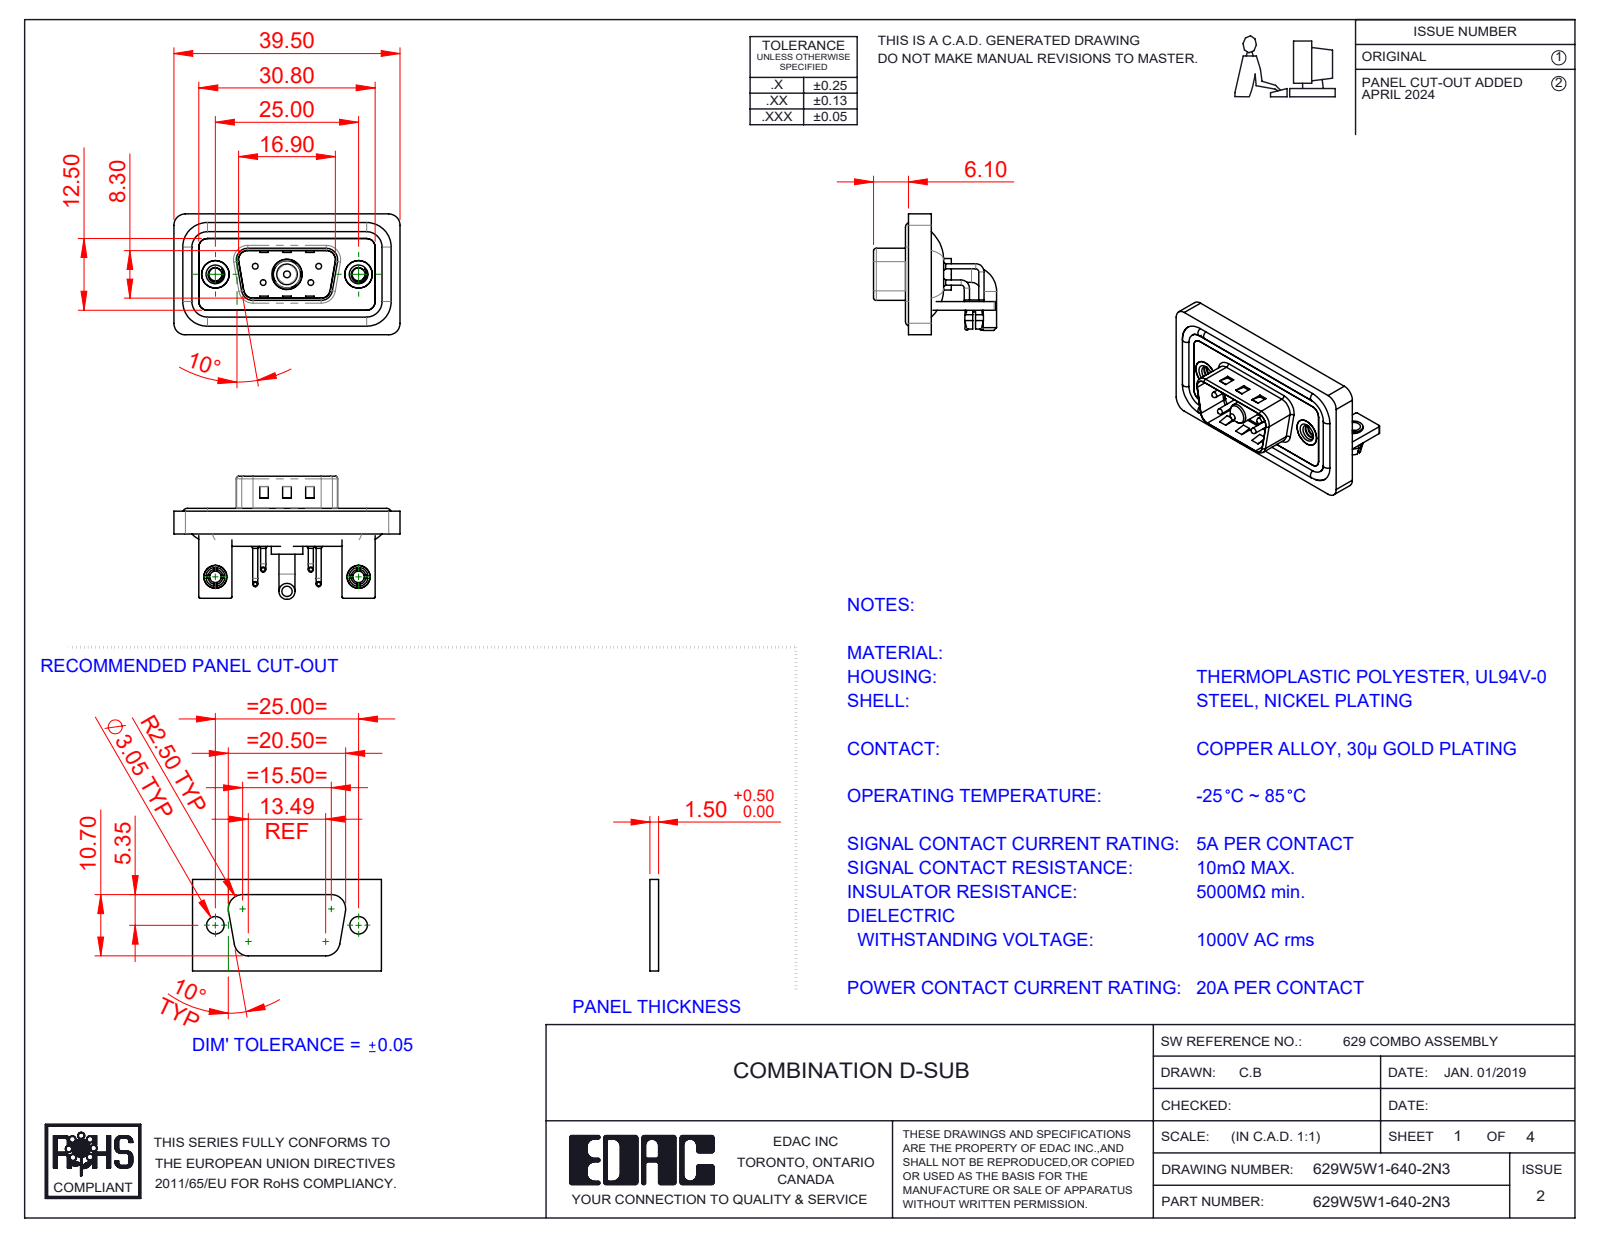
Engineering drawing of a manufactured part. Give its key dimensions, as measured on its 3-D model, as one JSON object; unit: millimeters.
{"part_name": "629Combo Threaded Rivet_3; 629Combo Stabilizer Bracket; 629Combo Housing_5W1; 629Combo Shell Front_09 Contacts (+7 more)", "step_written_by": "SolidWorks 2023 (CONFIG_CONTROL_DESIGN)", "units": "millimeters", "bodies": {"solids": 17, "faces": 1026, "planar": 479, "cylindrical": 395, "other": 152}, "overall_size": [39.5, 21.5, 21.1], "volume_mm3": 4790, "surface_area_mm2": 7961, "round_holes": [[2, 6], [0.75, 4], [1.6, 4], [2.26, 2], [2.5, 2], [3.2, 2], [4, 2], [4.8, 2], [5, 2], [4.85, 1], [5.3, 1]], "round_bosses_or_shafts": [[0.9, 8], [1.6, 4], [1.5, 4], [1, 4], [0.65, 4], [4.9, 2], [4, 2], [3.4, 2]], "partial_cylinders_radius": [[2, 19], [1.5, 18], [0.25, 16], [0.5, 9], [1.6, 8], [0.6, 4], [0.65, 4], [0.9, 4]], "face_to_face_distances": [0.4, 1.5, 0.8, 2.9, 1.1, 2.1, 1.2, 1.6, 2.5, 3.7], "hole_center_spacings": [3.16, 5.72, 7.1, 12.5, 18.1, 25, 4.39, 4.4]}
